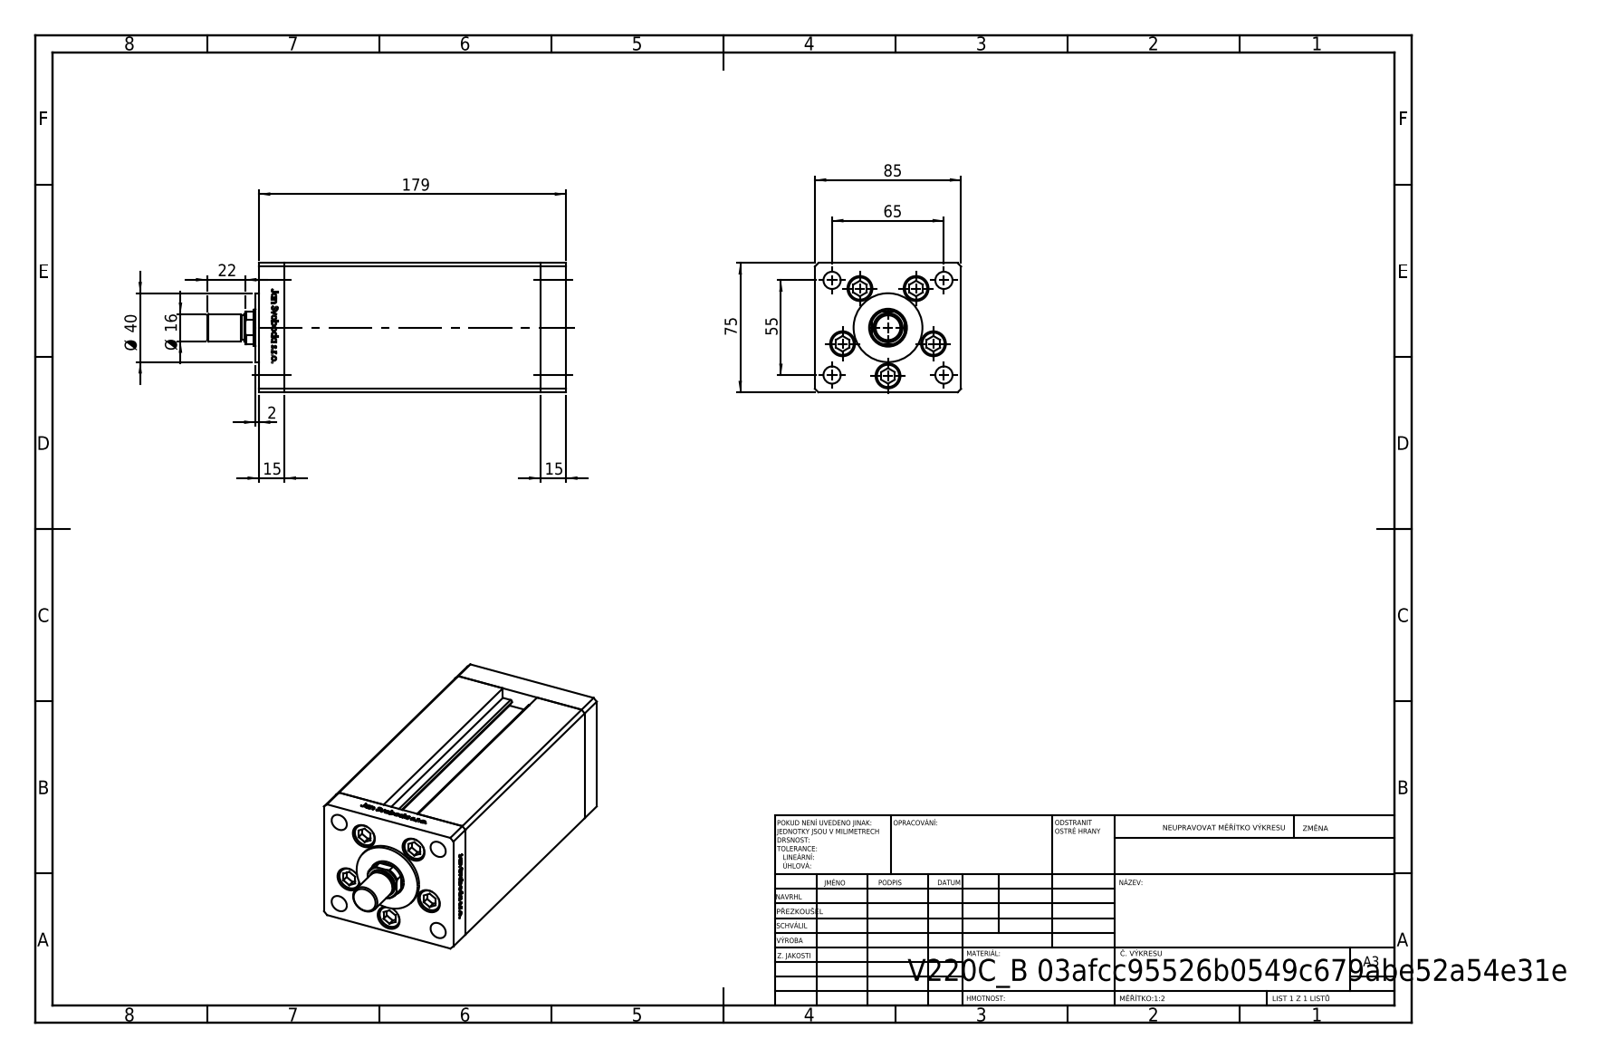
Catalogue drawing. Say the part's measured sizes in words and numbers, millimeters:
The part is named "V220C_B_VC; V220C_B MIDDLE; V220C_FRONT_B; V220CC_MALE_METRIC (+2 more)". Its 3-D file was written by "SolidWorks 2019 (CONFIG_CONTROL_DESIGN)". It is 15 solids with 1191 faces: 466 planar, 147 cylindrical and 578 other. Overall it measures 208.5 by 85 by 75 millimeters. Its volume is 1 014 000 cubic millimeters and its surface area 159 786 square millimeters. Round holes: 5 of diameter 11, 5 of diameter 14.5, 4 of diameter 10, 2 of diameter 2, 2 of diameter 13.16, 1 of diameter 15, 1 of diameter 22. Round bosses or shafts: 5 of diameter 8, 1 of diameter 40, 1 of diameter 16, 1 of diameter 14. Partial cylindrical surfaces (rounded edges, fillets, slot ends): 2 of radius 0.93, 1 of radius 10.5. The main face-to-face distances are 85, 75, 148.5, 15, 163.5, 178.5, 68.5, 9, 64.5, 10.5. The hole center spacings are 28, 42.57, 16.86, 19.17, 32.33, 32.5, 33.63, 37.33.
